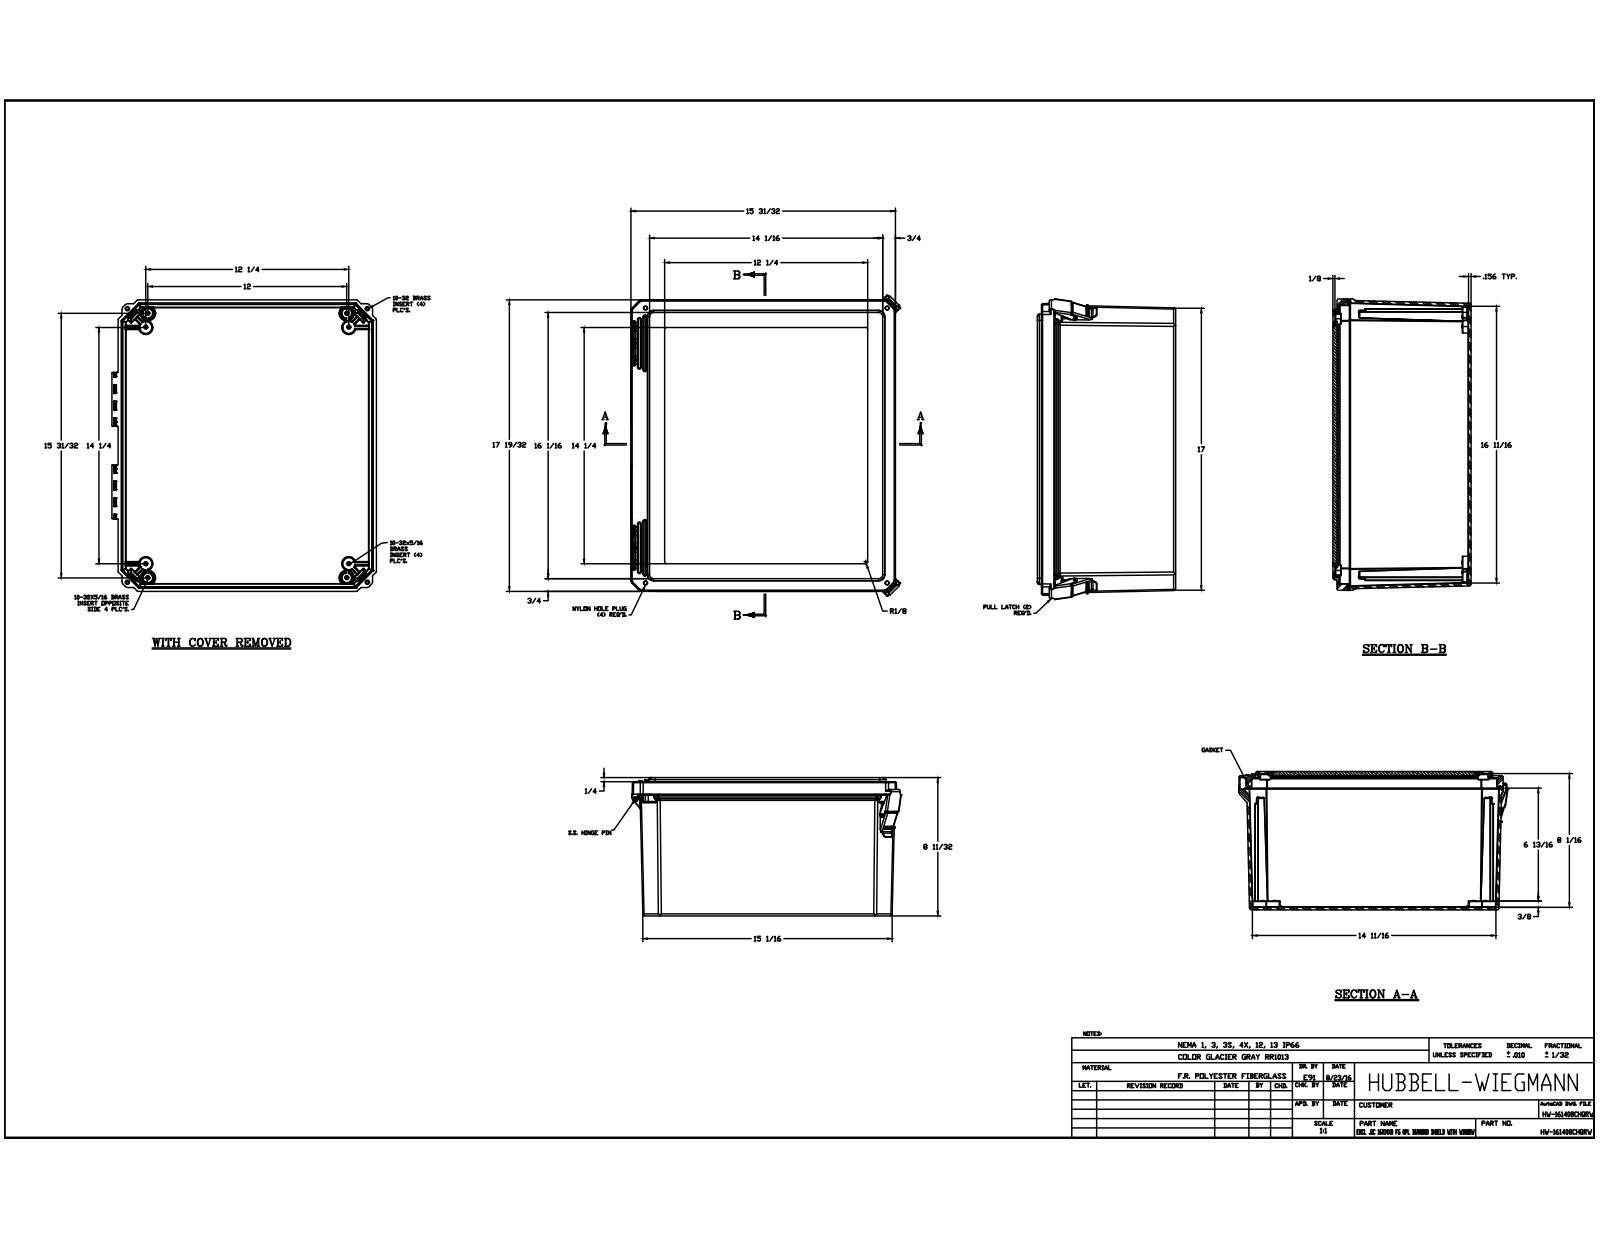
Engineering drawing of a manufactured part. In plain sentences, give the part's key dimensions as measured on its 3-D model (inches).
The part is named "HW-161408CHQRW; DS161408BOX; BRASS INSERT-(; BRASS INSERT-(_1 (+8 more)". Its 3-D file was written by "Autodesk Inventor 2017 (AUTOMOTIVE_DESIGN)". It is 34 solids with 2314 faces: 826 planar, 920 cylindrical and 568 other. Overall it measures 18.255 by 16.3 by 8.341 inches. Its volume is 203.7 cubic inches and its surface area 2 299 square inches. Round holes: 16 of diameter 0.156, 9 of diameter 0.135, 8 of diameter 0.152, 4 of diameter 0.15, 4 of diameter 0.252, 4 of diameter 0.253, 2 of diameter 0.135, 2 of diameter 0.219, 2 of diameter 0.227, 2 of diameter 0.313, 2 of diameter 0.375, 1 of diameter 0.137. Round bosses or shafts: 16 of diameter 0.246, 4 of diameter 0.3, 4 of diameter 0.209, 3 of diameter 0.135, 1 of diameter 0.435, 1 of diameter 0.435. Partial cylindrical surfaces (rounded edges, fillets, slot ends): 175 of radius 0.01, 80 of radius 0.005, 65 of radius 0.03, 57 of radius 0.02, 35 of radius 0.06, 26 of radius 0.063, 26 of radius 0.09, 26 of radius 0.125. The main face-to-face distances are 0.156, 8.185, 8.341, 0.18, 0.181, 8.117, 7.961, 0.225, 0.125, 0.25. The hole center spacings are 0.25, 1.33, 21.012, 0.865, 1.652, 12.155, 13.296, 13.469.
